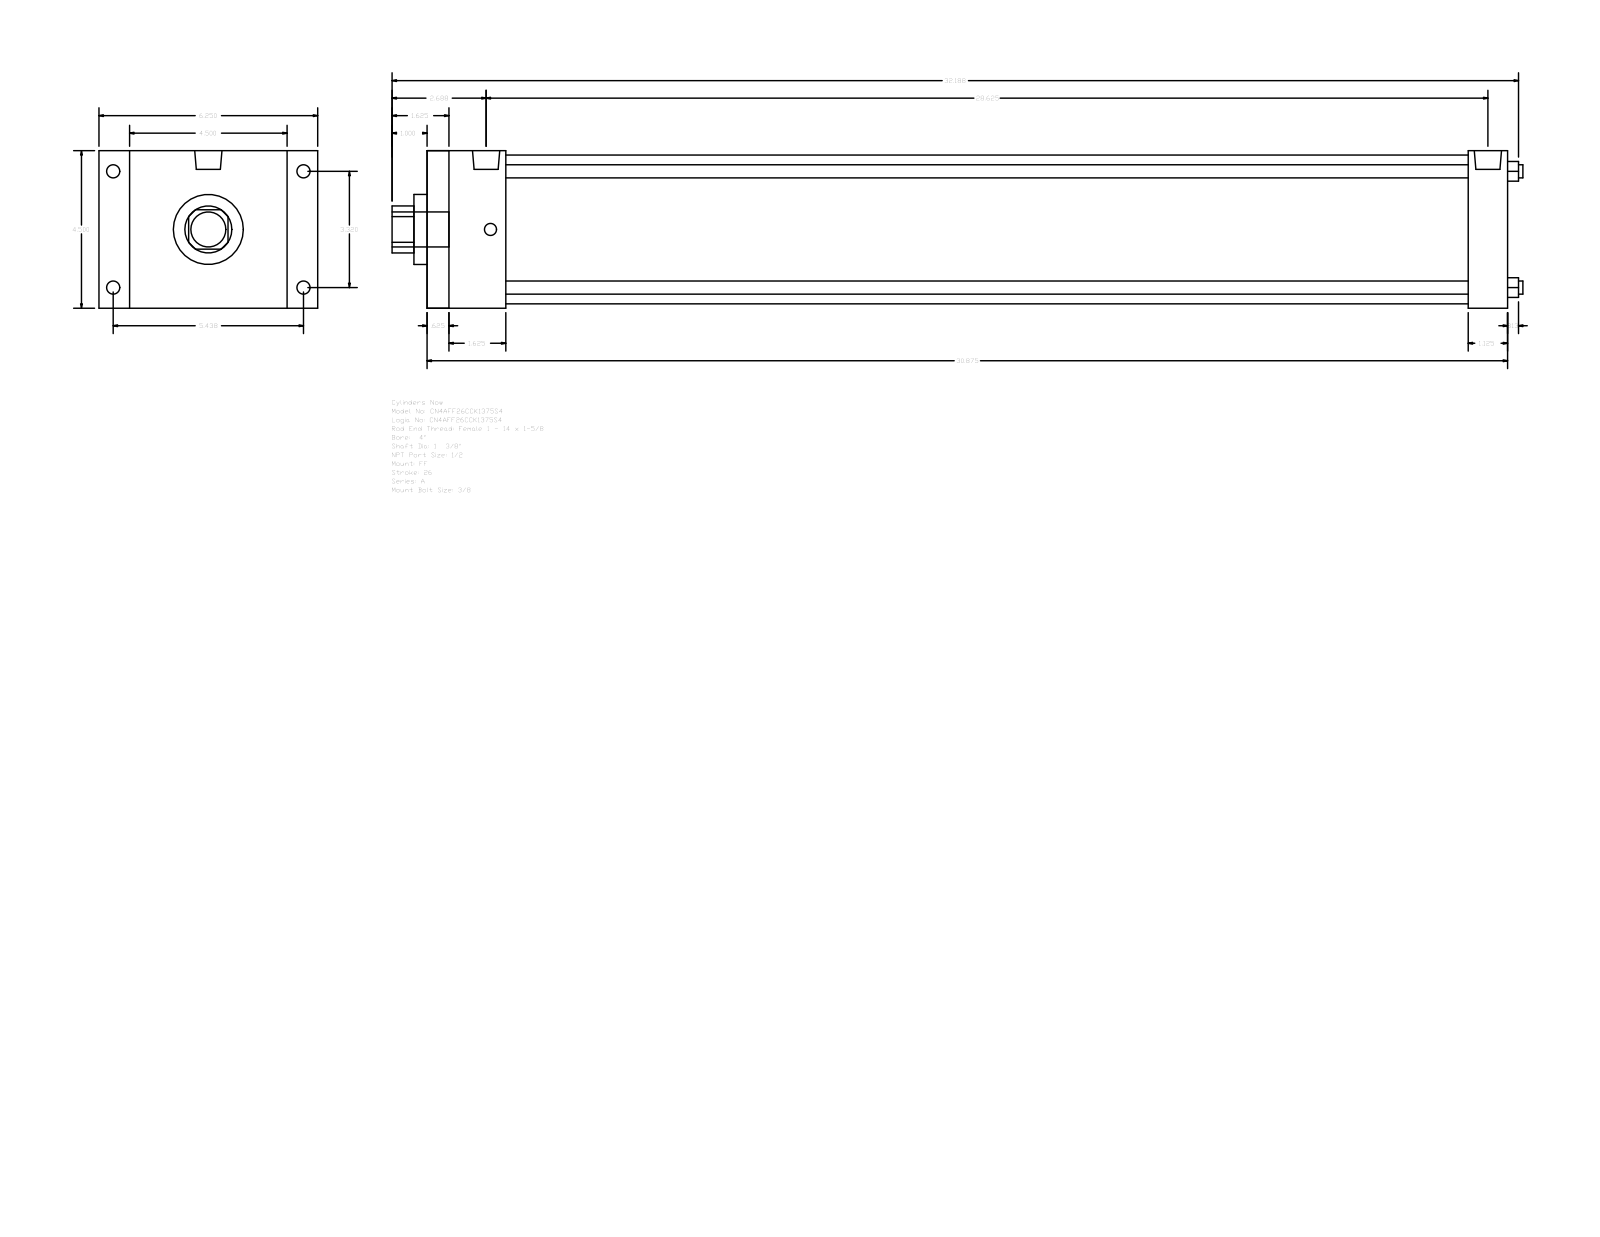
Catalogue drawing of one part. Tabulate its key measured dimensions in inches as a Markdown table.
| quantity | value |
| --- | --- |
| part name | A_FF__0400_1.375 |
| STEP written by | GSSL Pune (CONFIG_CONTROL_DESIGN) |
| units | inches |
| bodies | 0 solids, 92 faces (64 planar, 28 cylindrical, 0 other) |
| overall size | 32.313 × 6.25 × 4.5 |
| round holes (diameter × count) | 0.375 × 4, 1.375 × 1, 2 × 1, 4.25 × 1 |
| round bosses / shafts (diameter × count) | 0.375 × 4, 0.344 × 4, 0.778 × 2, 1 × 1 |
| partial cylindrical surfaces (radius × count) | 0.672 × 1 |
| main face-to-face distances | 4.5, 30.875, 30.25, 0.625, 1.125, 0.875, 5.375, 29.75, 29.125, 2.25 |
| hole center spacings | 2.347, 3.32, 4.695 |
